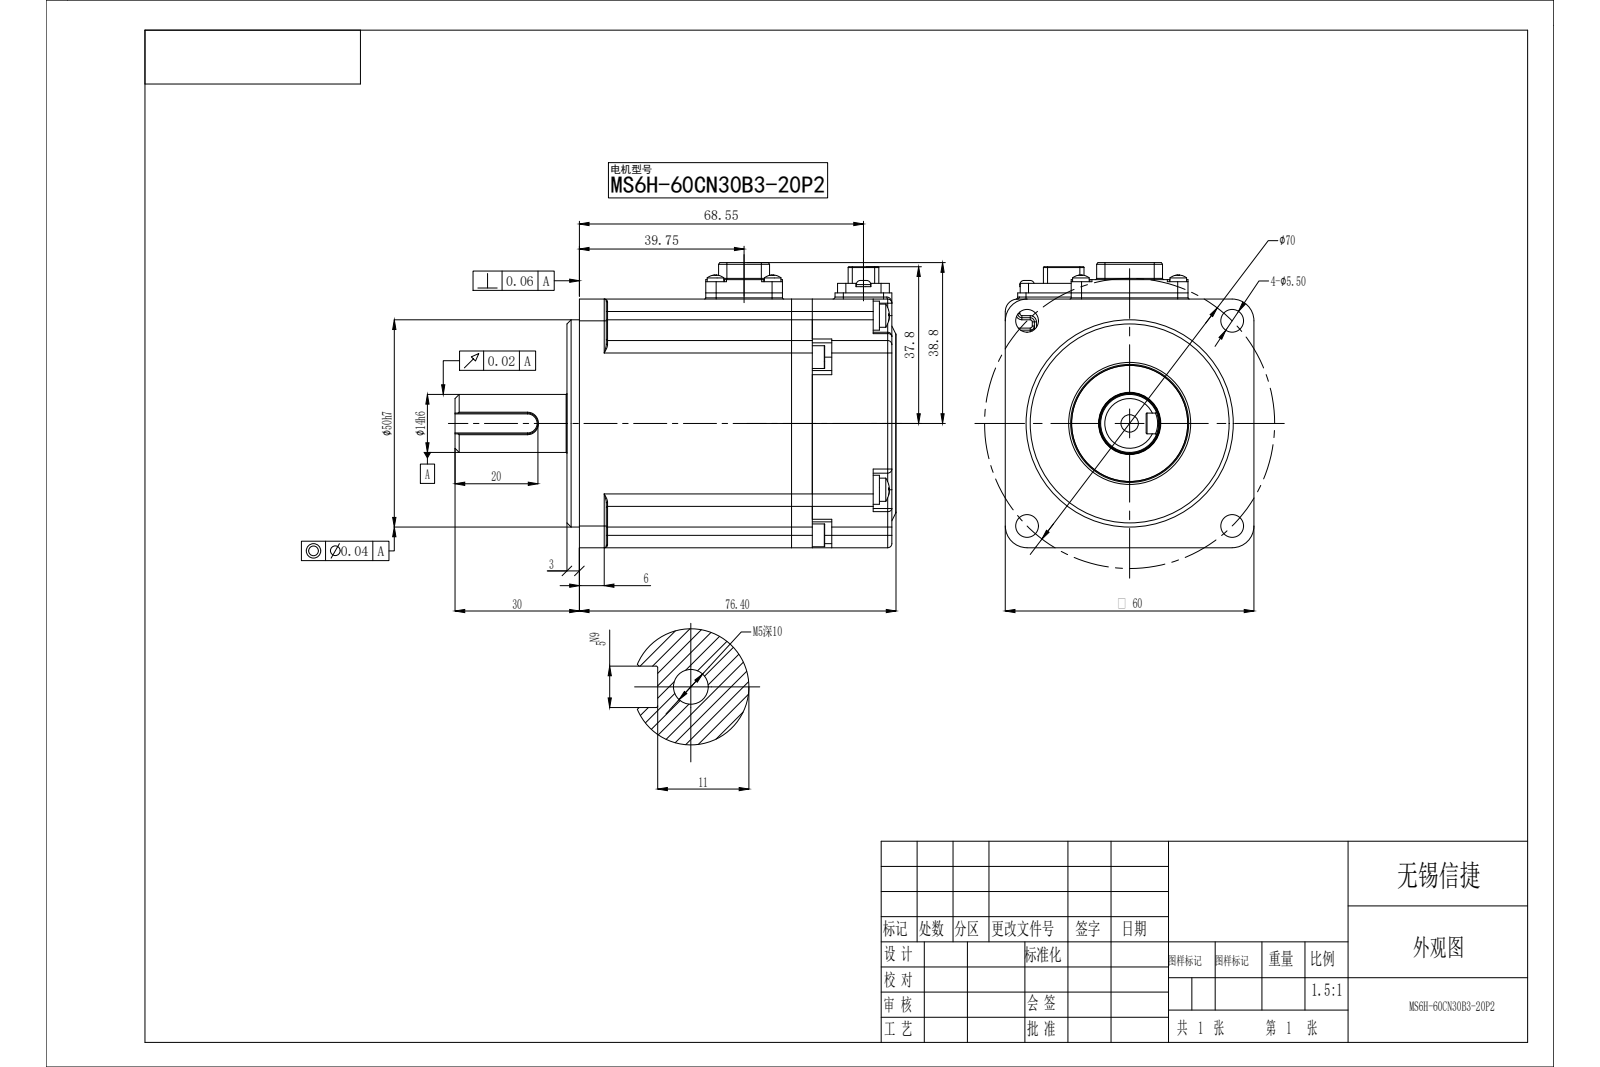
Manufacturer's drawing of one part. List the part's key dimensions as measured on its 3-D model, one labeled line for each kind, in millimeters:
STEP written by: SolidWorks 2016 (CONFIG_CONTROL_DESIGN)
Units: millimetres
Bodies: 0 solids, 775 faces (386 planar, 255 cylindrical, 134 other)
Overall size (bounding box): 106.4 × 68.8 × 60
Round holes (diameter × count): ⌀2.1 ×4, ⌀5.5 ×4, ⌀1.6 ×2, ⌀4.2 ×1, ⌀15 ×1
Round bosses / shafts (diameter × count): ⌀7 ×4, ⌀5.6 ×4, ⌀5.5 ×4, ⌀4 ×4, ⌀3.5 ×2, ⌀50 ×1, ⌀28 ×1, ⌀14 ×1
Partial cylindrical surfaces — rounded edges, fillets, slot ends (radius × count): R1 ×37, R0.5 ×25, R0.3 ×21, R0.2 ×17, R2 ×12, R3 ×9, R2.5 ×5, R0.6 ×4
Main face-to-face distances: 60, 3, 79.4, 76.4, 75.4, 54.2, 78.4, 1, 51.2, 24.2
Hole centre spacings: 8, 16.6, 18.43, 34.99, 35, 49.49, 49.5, 70
